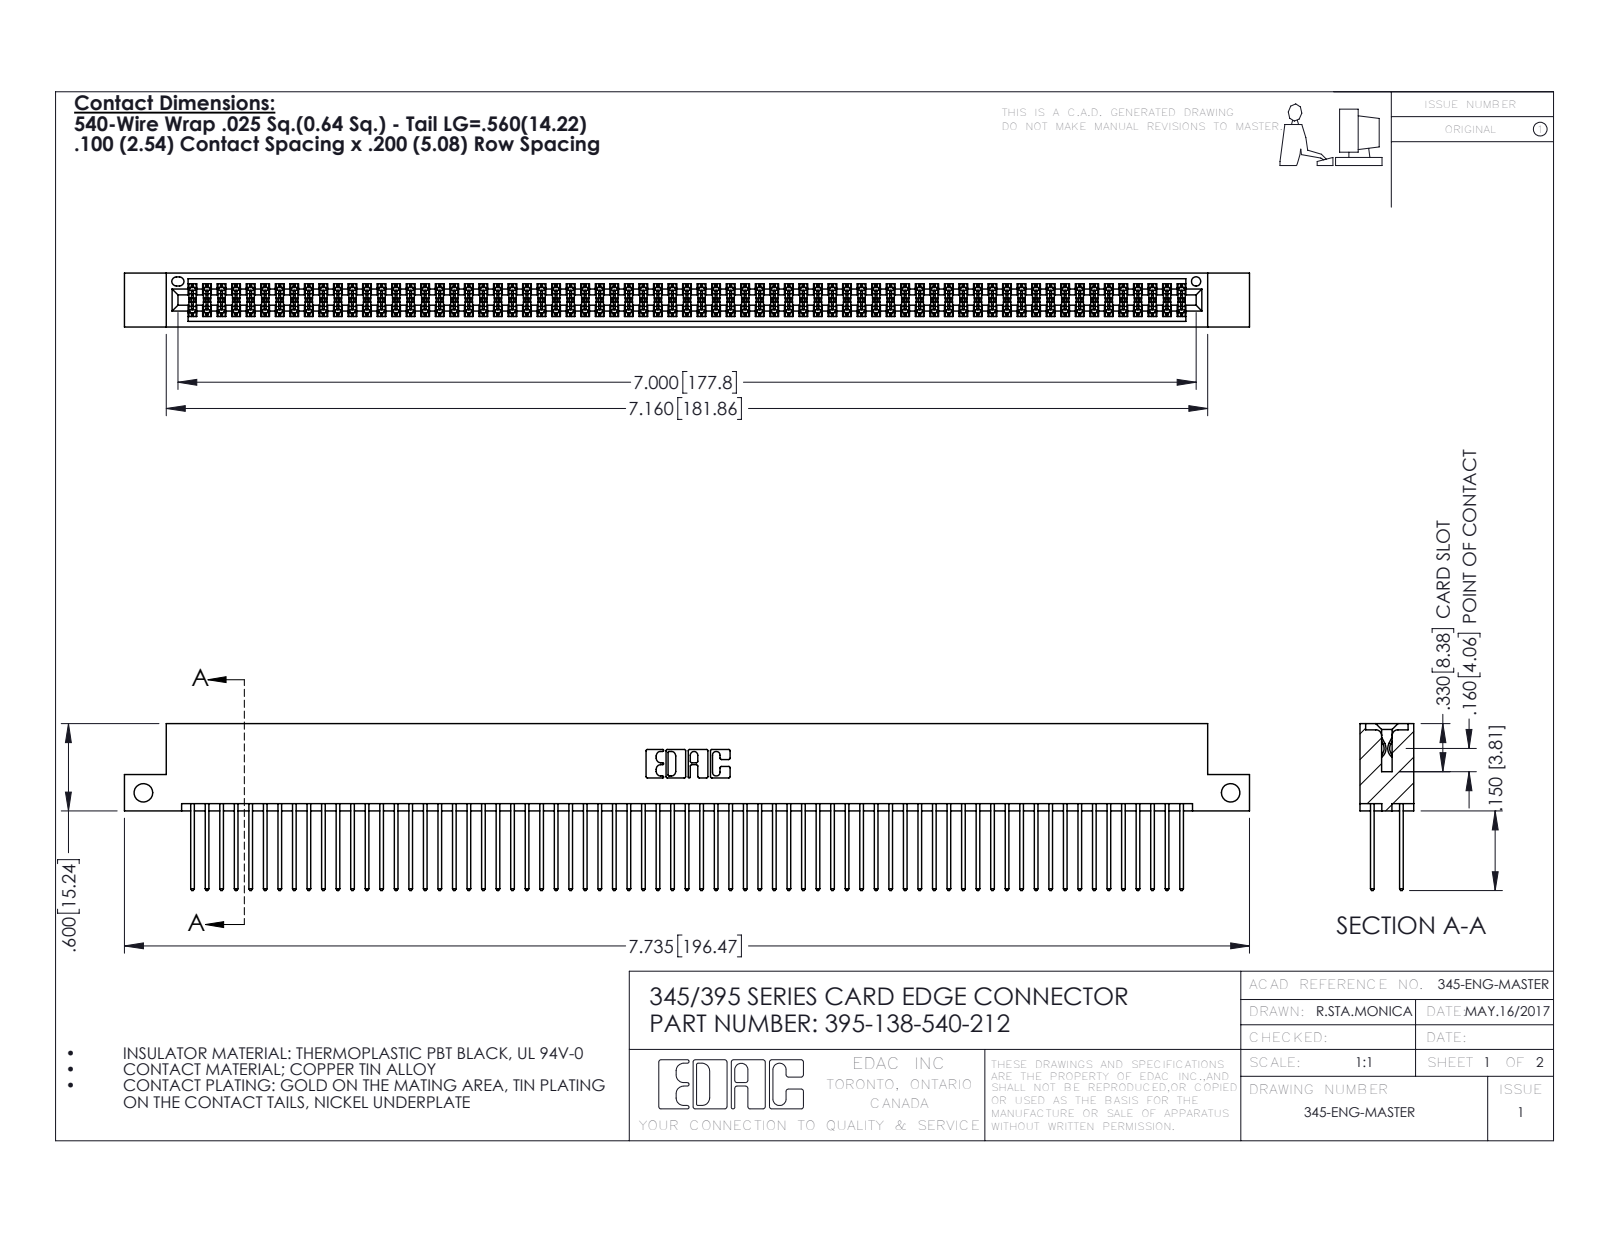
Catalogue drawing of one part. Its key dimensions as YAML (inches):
part_name: "345-292-001_345-293-140; 345 Part_Flush Mounting Lugs - Side Mount; 395-138-540-212"
step_written_by: "SolidWorks 2016 (CONFIG_CONTROL_DESIGN)"
units: inches
bodies: {solids: 139, faces: 7026, planar: 4634, cylindrical: 2392, other: 0}
overall_size: [7.735, 1.147, 0.37]
volume: 1.207
surface_area: 49.66
round_holes:
  - {diameter: 0.128, count: 2}
  - {diameter: 0.064, count: 1}
partial_cylinders:
  - {radius: 0.006, count: 207}
  - {radius: 0.01, count: 138}
  - {radius: 0.01, count: 22}
  - {radius: 0.007, count: 6}
  - {radius: 0.031, count: 6}
  - {radius: 0.026, count: 3}
  - {radius: 0.014, count: 2}
  - {radius: 0.019, count: 2}
face_to_face_distances: [0.298, 0.072, 0.2, 0.098, 0.272, 0.025, 0.225, 0.37, 0.175, 0.149]
hole_center_spacings: [7.475]
